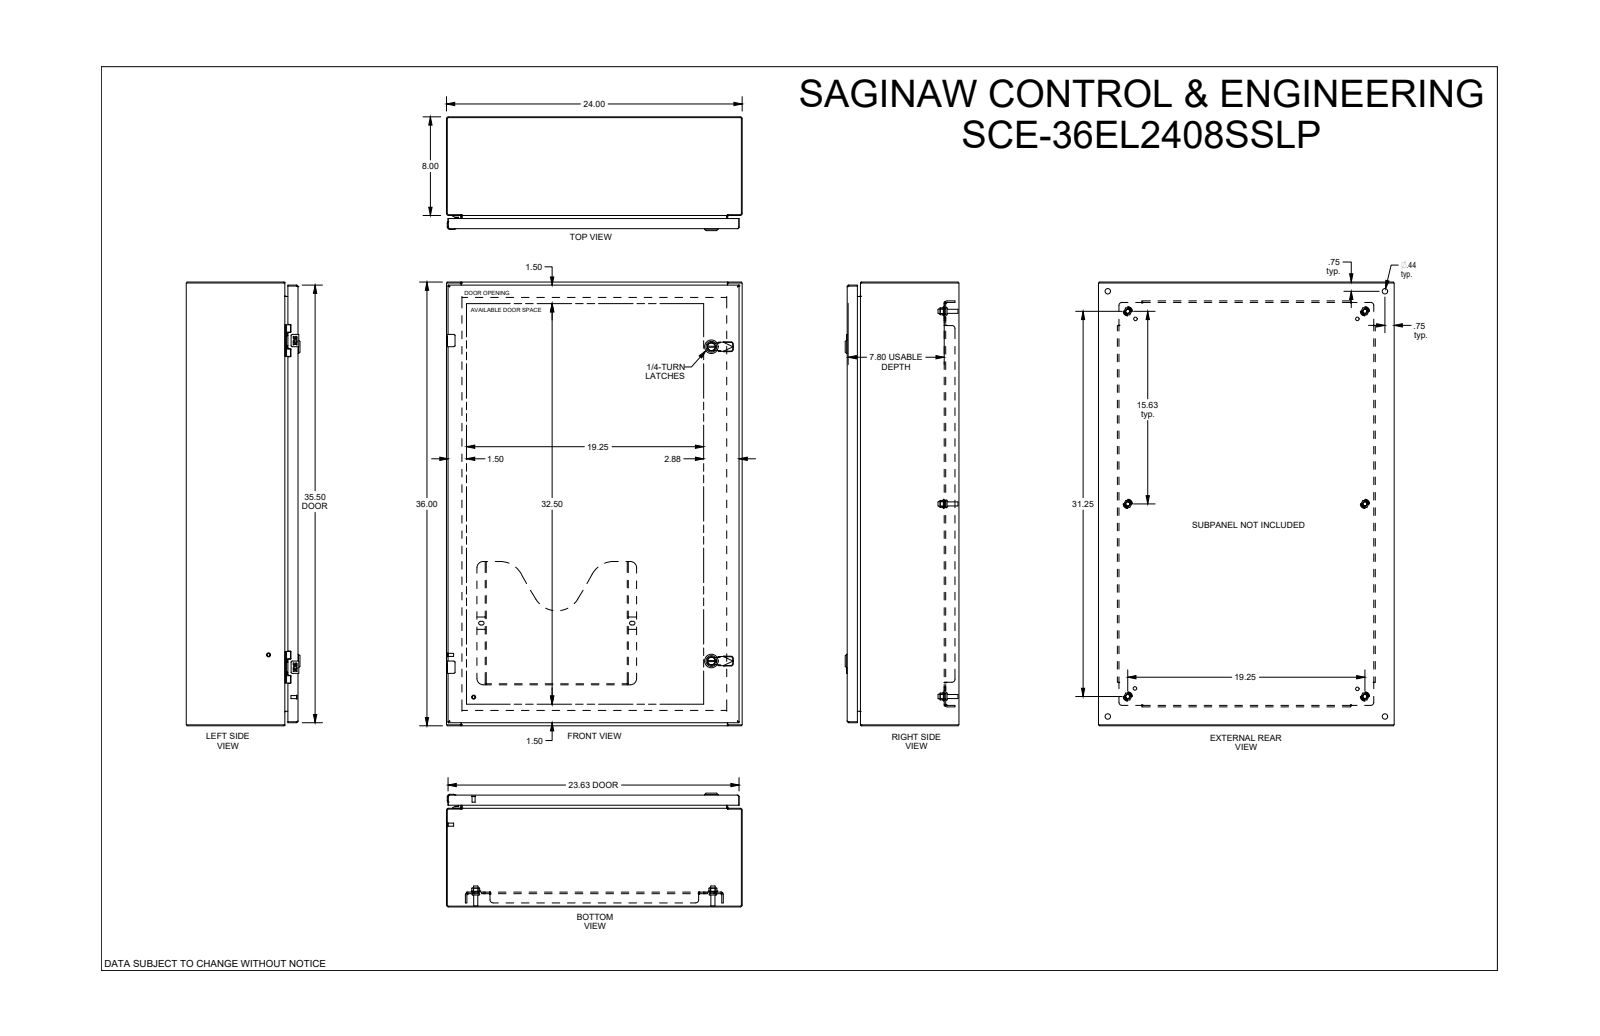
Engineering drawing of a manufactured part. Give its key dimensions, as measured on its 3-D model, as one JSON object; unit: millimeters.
{"part_name": "SCE-36EL2408SSLP", "step_written_by": "SolidWorks 2019 (CONFIG_CONTROL_DESIGN)", "units": "millimeters", "bodies": {"solids": 0, "faces": 2948, "planar": 1331, "cylindrical": 779, "other": 838}, "overall_size": [914.4, 609.6, 234.4], "round_holes": [[9.3, 6], [12.7, 6], [4.4, 4], [5.2, 4], [6.2, 4], [6.8, 4], [7.1, 4], [9.5, 4], [11.1, 4], [4, 2], [5, 2], [5.5, 2]], "round_bosses_or_shafts": [[9.3, 6], [8.4, 6], [4.3, 6], [6.4, 4], [6.3, 4], [5, 3], [28, 2], [22, 2]], "partial_cylinders_radius": [[0.3, 56], [0.3, 40], [0.4, 32], [1, 23], [0.5, 20], [0.7, 12], [1.8, 10], [3.7, 10]], "face_to_face_distances": [1.9, 1.9, 226.6, 228.5, 230.5, 228.5, 30.5, 200, 25.4, 3.2], "hole_center_spacings": [673.1, 25, 0.5, 58.4, 114.1, 396.9, 440.1, 531.8]}
